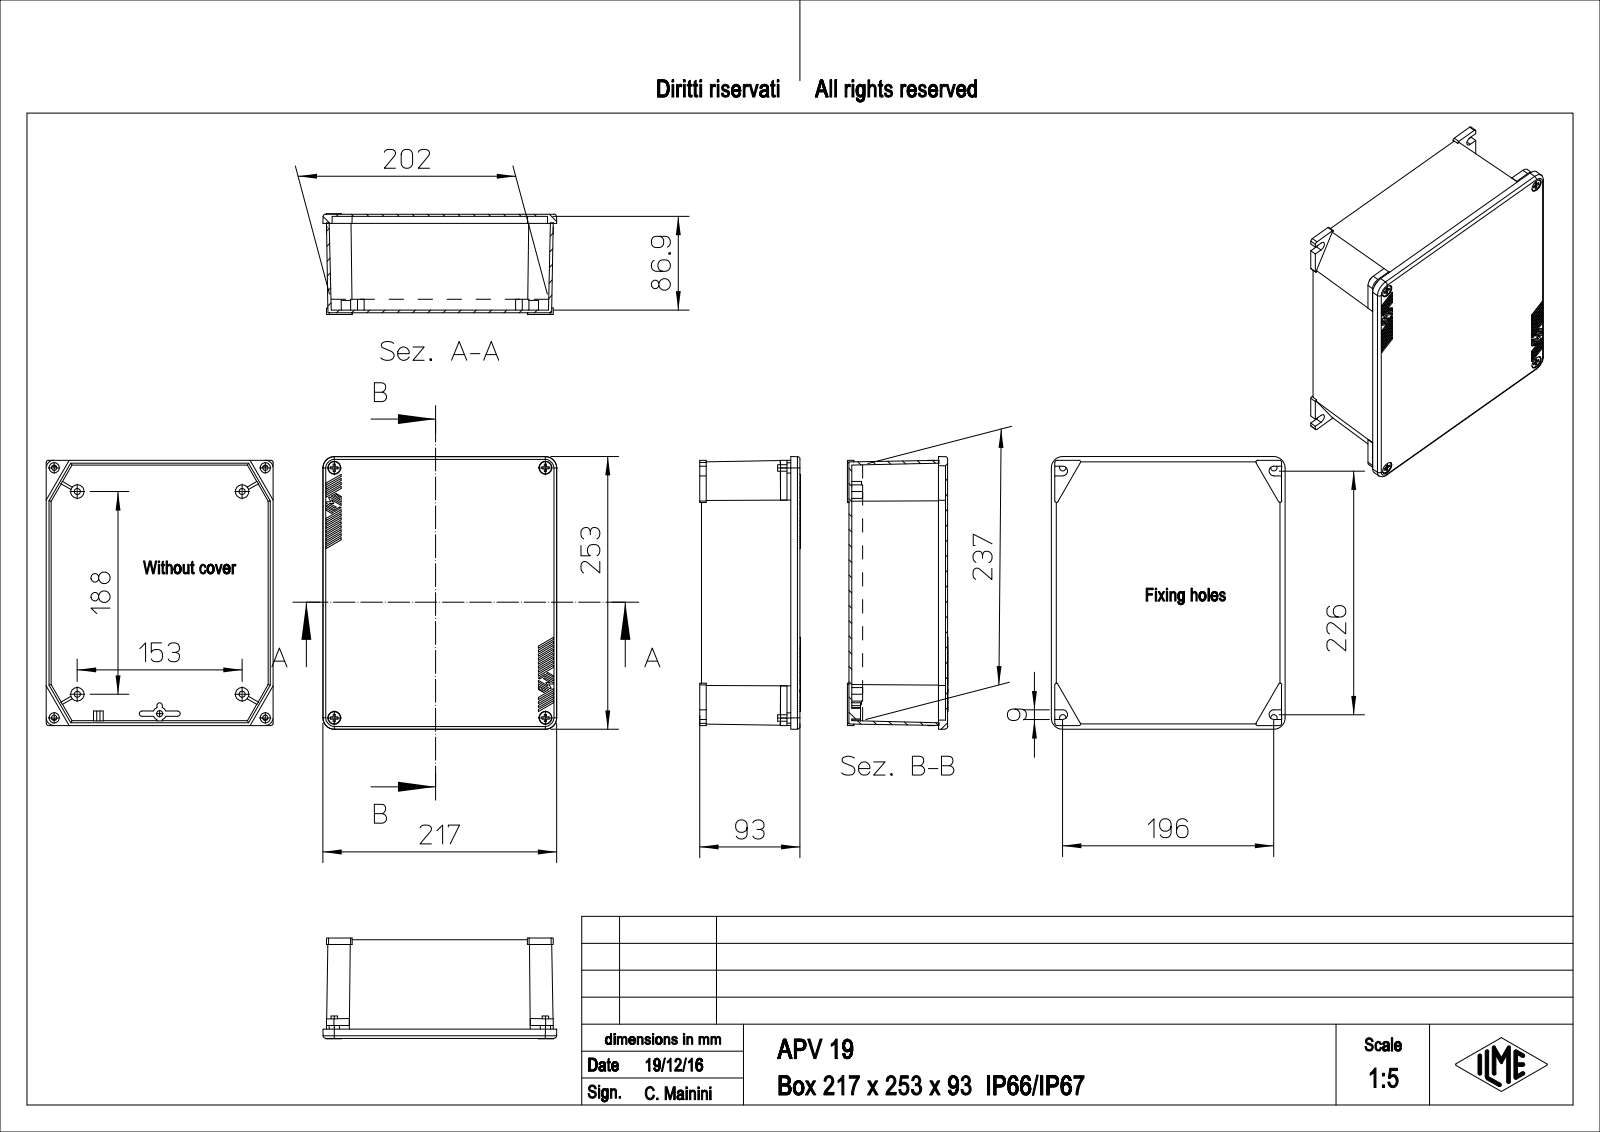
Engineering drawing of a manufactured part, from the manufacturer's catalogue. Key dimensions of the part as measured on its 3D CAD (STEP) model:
Part name (STEP PRODUCT): COPERCHIO; CASSETA; VITE_TE_M6X20.3; APV_19
STEP written by: CoCreate Modeling 16.00A 16-Aug-2008 (C) Parametric Technology GmbH (AUTOMOTIVE_DESIGN)
Units: millimetres
Bodies: 6 solids, 1485 faces (1196 planar, 241 cylindrical, 48 other)
Overall size (bounding box): 253 × 217 × 92.15
Volume: 645 506 mm³ · Surface area: 376 024 mm²
Round holes (diameter × count): ⌀3.4 ×6, ⌀5 ×4, ⌀6.5 ×4, ⌀12 ×4, ⌀5.82 ×2
Round bosses / shafts (diameter × count): ⌀12.5 ×4, ⌀9.5 ×4, ⌀6 ×4, ⌀5.4 ×4, ⌀6.2 ×2, ⌀10 ×1
Partial cylindrical surfaces — rounded edges, fillets, slot ends (radius × count): R3 ×24, R0.33 ×22, R2 ×16, R0.17 ×6, R0.27 ×4, R0.37 ×4, R1.5 ×4, R2.1 ×4
Main face-to-face distances: 90.25, 2, 88.25, 2.6, 85.65, 87.65, 5, 4.75, 205.75, 241
Hole centre spacings: 196, 30.76, 98.08, 175.88, 211.1, 232, 273.04, 303.71
